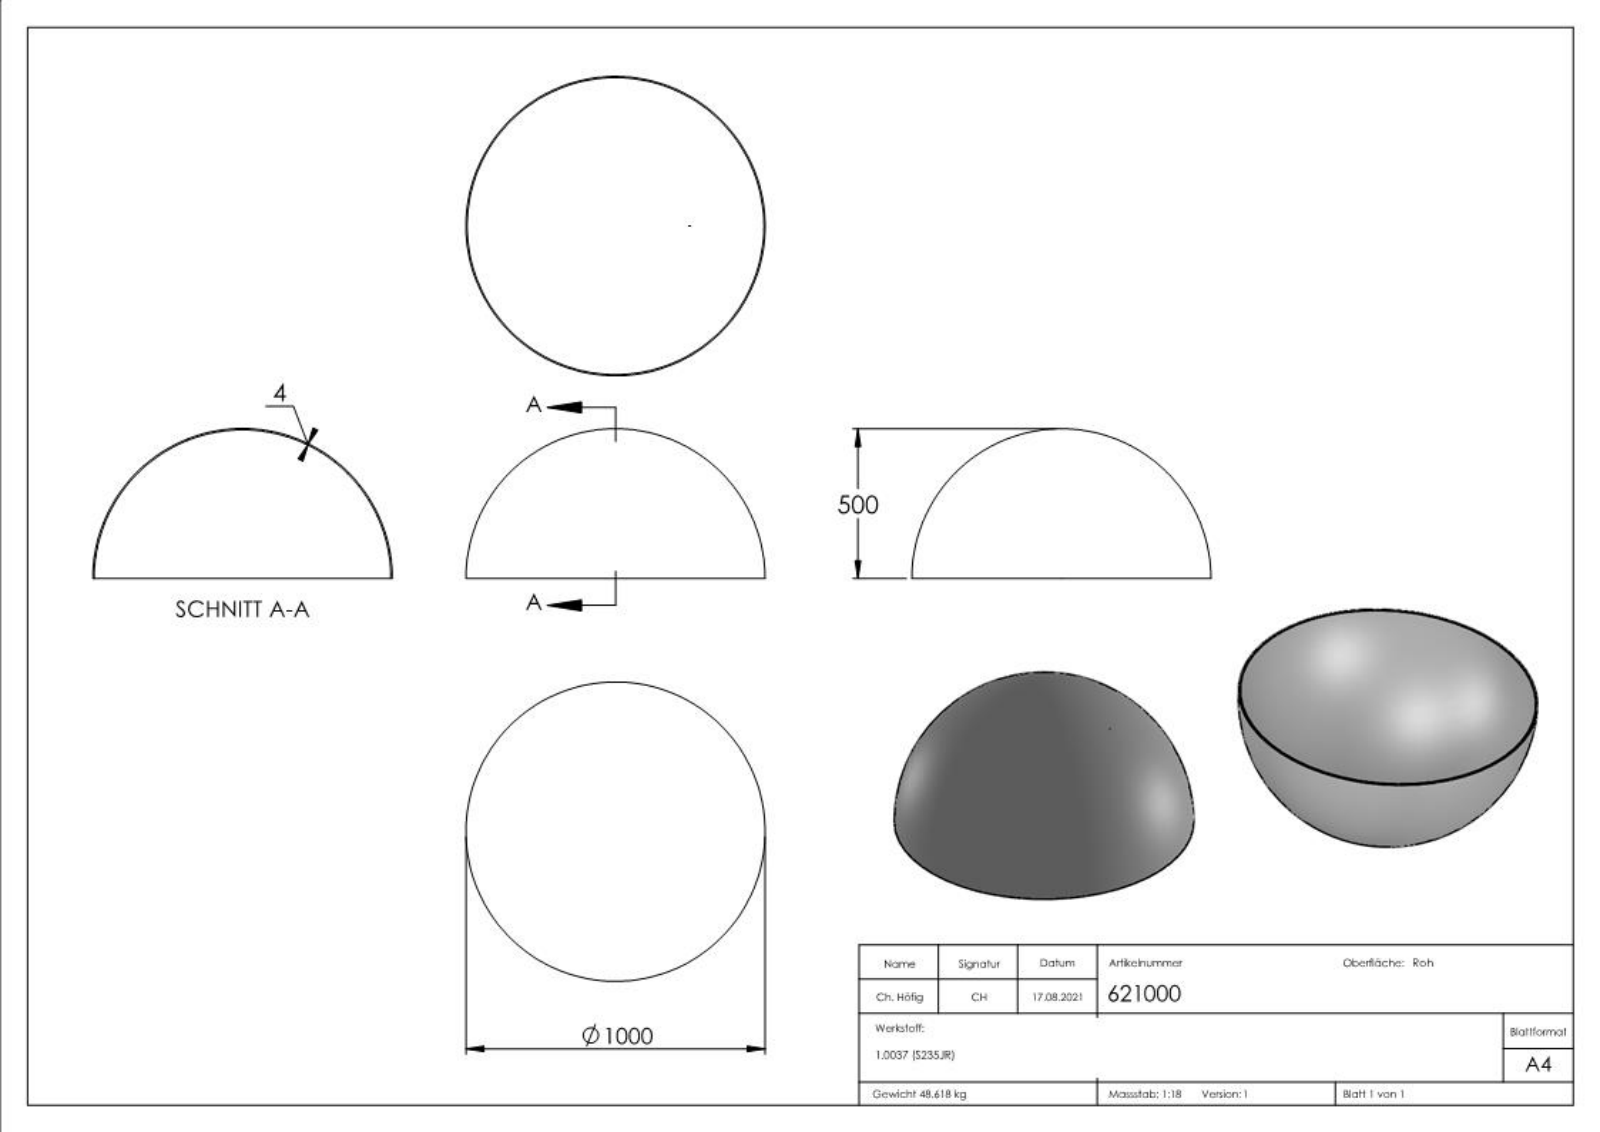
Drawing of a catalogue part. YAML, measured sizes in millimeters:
part_name: "621000"
step_written_by: "SolidWorks 2018 (CONFIG_CONTROL_DESIGN)"
units: millimeters
bodies: {solids: 1, faces: 183, planar: 70, cylindrical: 0, other: 113}
overall_size: [1000, 1000, 500]
volume: 6233000
surface_area: 3129000
face_to_face_distances: [1.19, 0.55, 0.5, 3.39, 3.89, 0.81, 1.31, 4.7, 0.66, 0.53]
